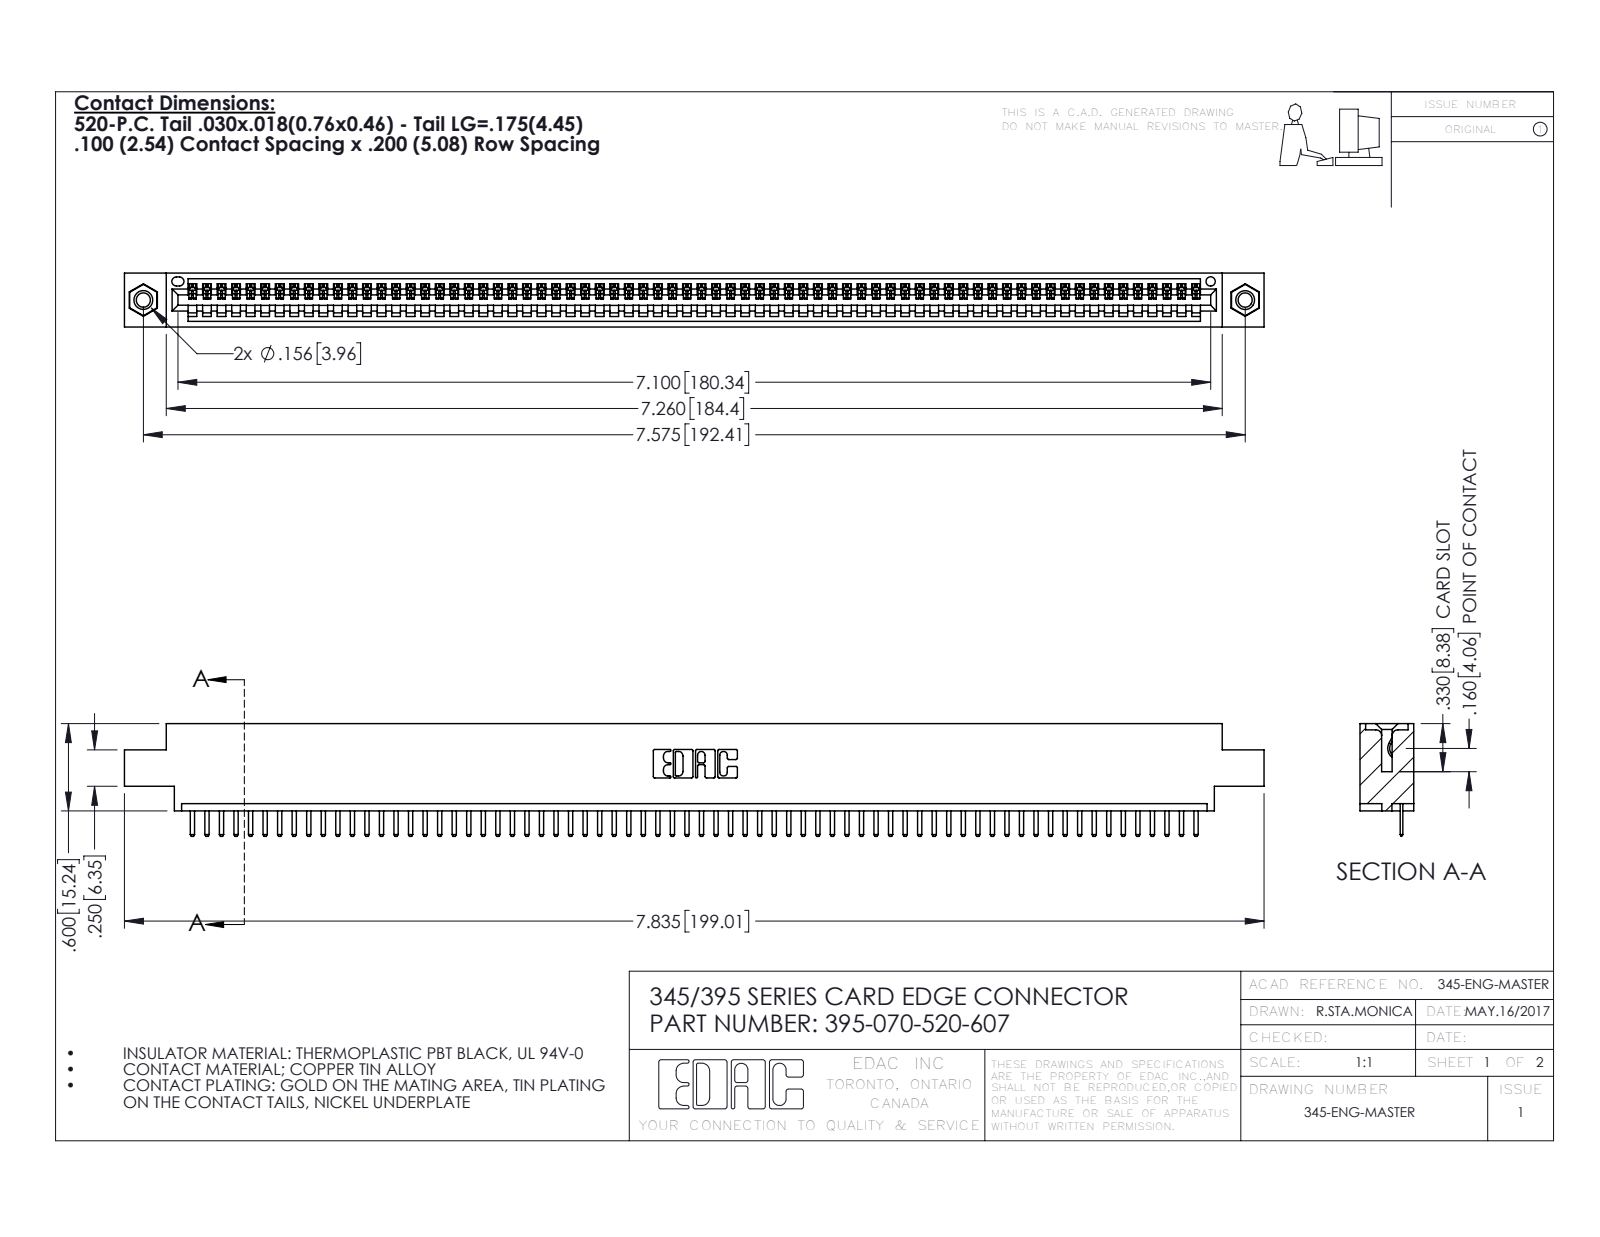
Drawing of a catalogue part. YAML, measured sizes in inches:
part_name: "345 Part_0.170 Offset - 0.156 Dia-TI; 395-070-520-607; 345-250-001_345-250-005-103; 345-292-001_345-293-120"
step_written_by: "SolidWorks 2016 (CONFIG_CONTROL_DESIGN)"
units: inches
bodies: {solids: 73, faces: 4530, planar: 3056, cylindrical: 1458, other: 16}
overall_size: [7.835, 0.775, 0.37]
volume: 1.147
surface_area: 38.55
round_holes:
  - {diameter: 0.098, count: 2}
  - {diameter: 0.125, count: 2}
  - {diameter: 0.156, count: 2}
  - {diameter: 0.064, count: 1}
round_bosses_or_shafts:
  - {diameter: 0.155, count: 2}
partial_cylinders:
  - {radius: 0.01, count: 142}
  - {radius: 0.006, count: 140}
  - {radius: 0.01, count: 22}
  - {radius: 0.007, count: 6}
  - {radius: 0.031, count: 6}
  - {radius: 0.026, count: 3}
  - {radius: 0.031, count: 2}
  - {radius: 0.04, count: 2}
face_to_face_distances: [0.072, 0.298, 0.37, 0.2, 0.098, 0.272, 0.025, 0.225, 0.072, 0.175]
hole_center_spacings: [0.27, 7.339, 7.575]
